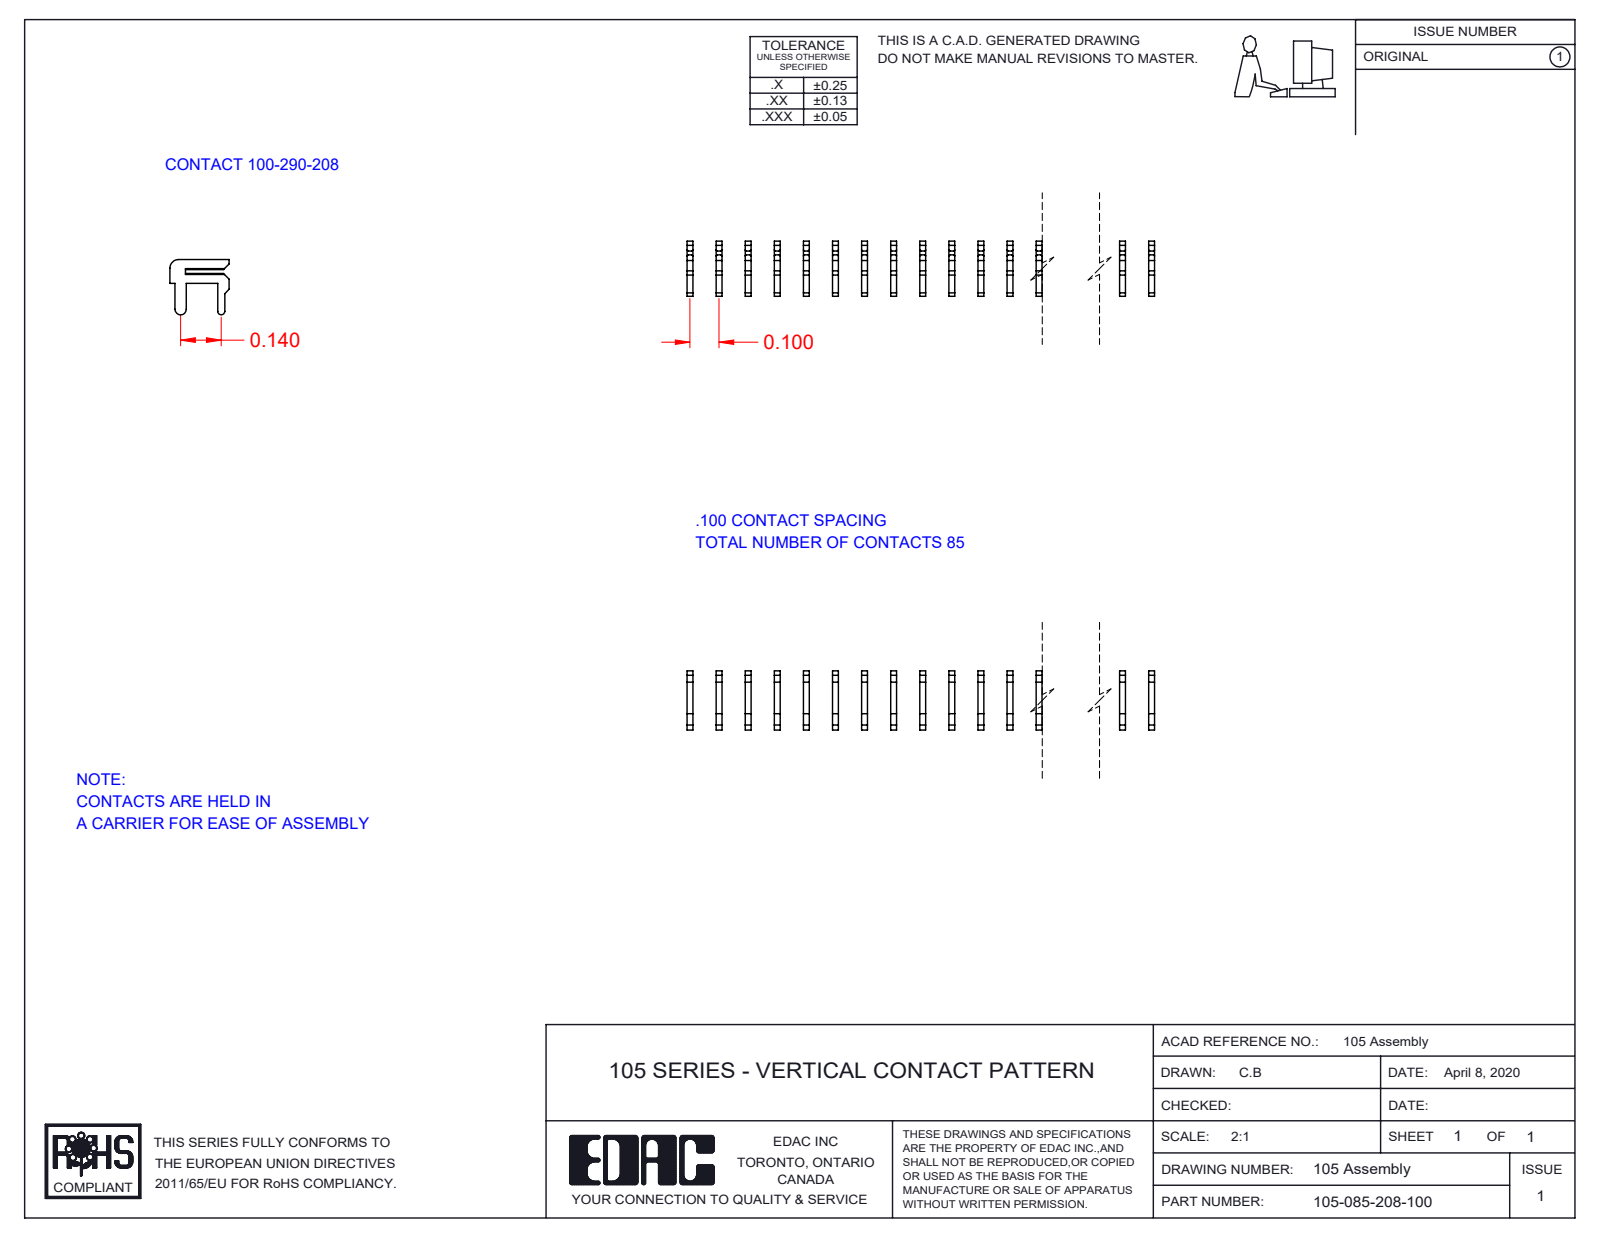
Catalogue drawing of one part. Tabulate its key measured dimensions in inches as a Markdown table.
| quantity | value |
| --- | --- |
| part name | 105-085-208-100; 100-290-001_100-290-208 |
| STEP written by | SolidWorks 2016 (CONFIG_CONTROL_DESIGN) |
| units | inches |
| bodies | 85 solids, 2125 faces (1870 planar, 255 cylindrical, 0 other) |
| overall size | 8.42 × 0.204 × 0.19 |
| volume | 0.036 in³ |
| surface area | 5.599 in² |
| partial cylindrical surfaces (radius × count) | 0.012 × 1, 0.019 × 1, 0.03 × 1 |
| main face-to-face distances | 0.1, 0.2, 0.3, 0.4, 0.5, 0.034, 0.048, 0.6, 0.7, 0.8 |
